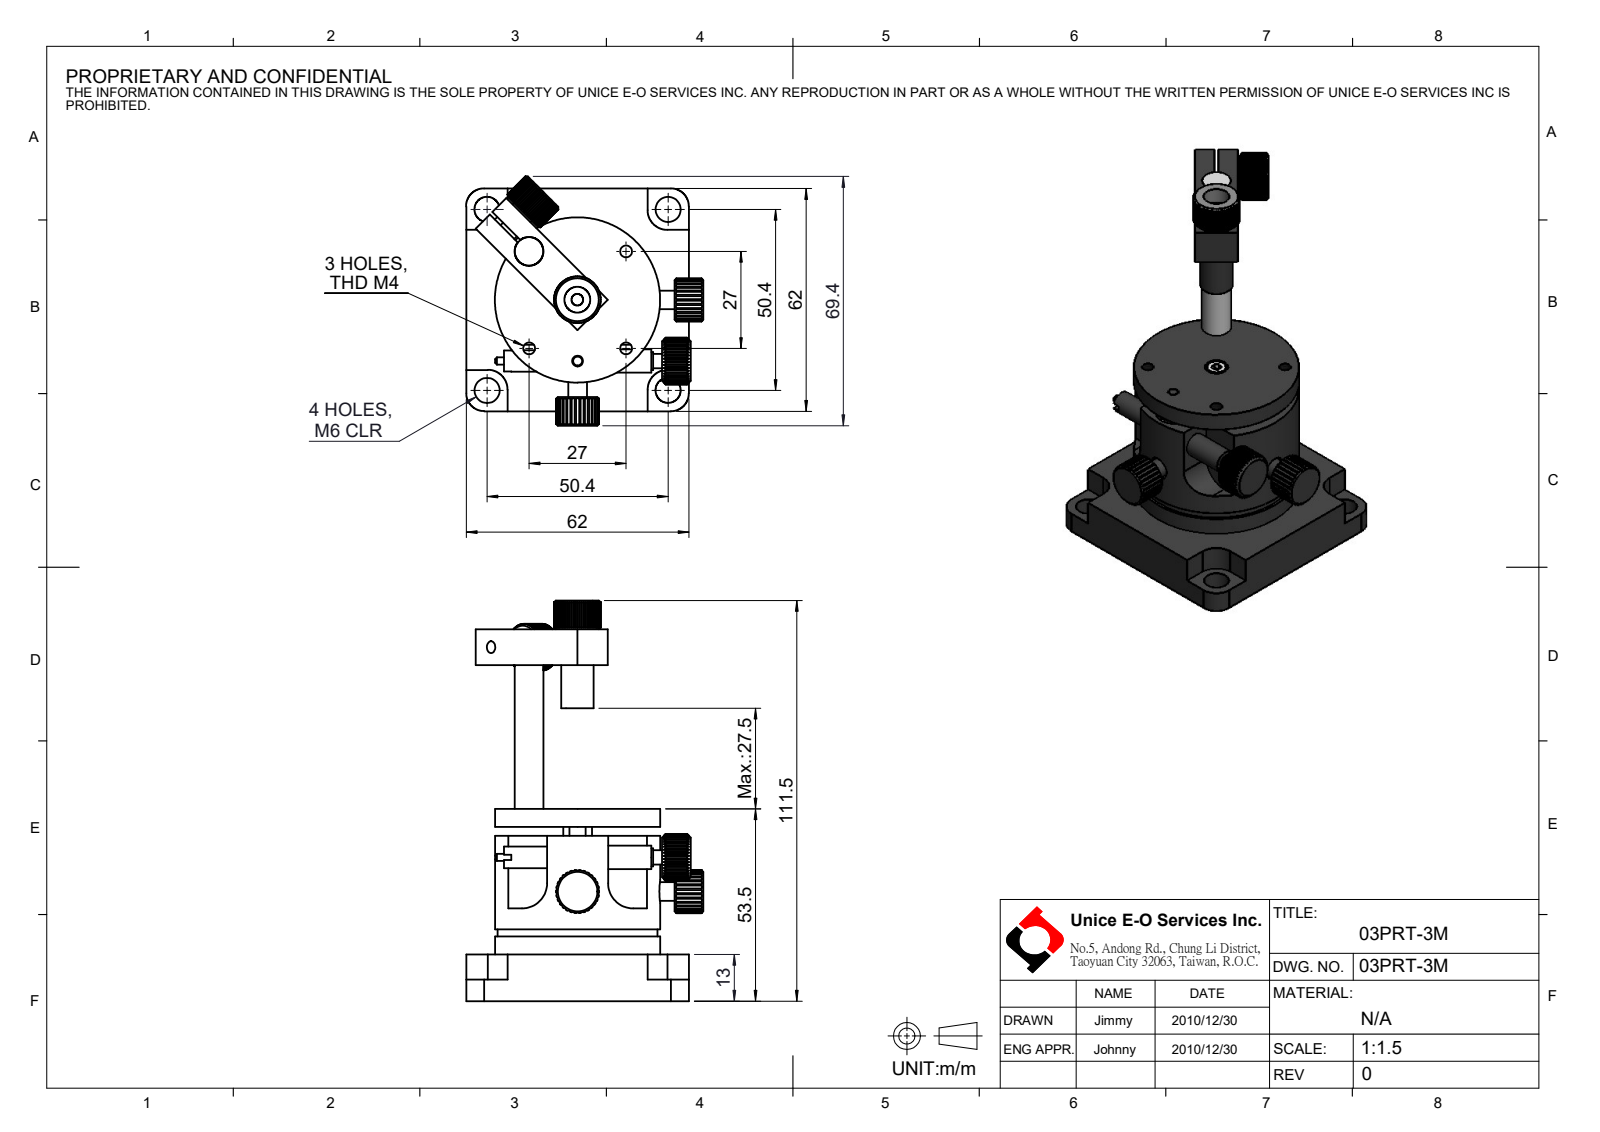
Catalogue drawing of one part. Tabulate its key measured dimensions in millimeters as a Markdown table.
| quantity | value |
| --- | --- |
| part name | 03PRT-3M |
| STEP written by | SolidWorks 2016 (CONFIG_CONTROL_DESIGN) |
| units | millimeters |
| bodies | 0 solids, 1120 faces (212 planar, 858 cylindrical, 50 other) |
| overall size | 111.5 × 69.36 × 66 |
| round holes (diameter × count) | 3.3 × 7, 6.5 × 4, 7 × 4, 8 × 4, 7.2 × 3, 2.1 × 1, 9.5 × 1 |
| round bosses / shafts (diameter × count) | 7 × 2, 6 × 2, 5.2 × 2, 2 × 2, 46 × 1, 44.5 × 1, 9 × 1, 8 × 1 |
| partial cylindrical surfaces (radius × count) | 0.1 × 166, 0.75 × 60, 5 × 4, 5.5 × 4, 6.5 × 4, 6 × 2, 7 × 2, 2.5 × 1 |
| main face-to-face distances | 13, 35.5, 5, 53.5, 40.5, 48.5, 33, 12, 7.5, 62 |
| hole center spacings | 39.78, 17.68, 26.02, 35.64, 40.43, 19.09, 17.96, 22 |
